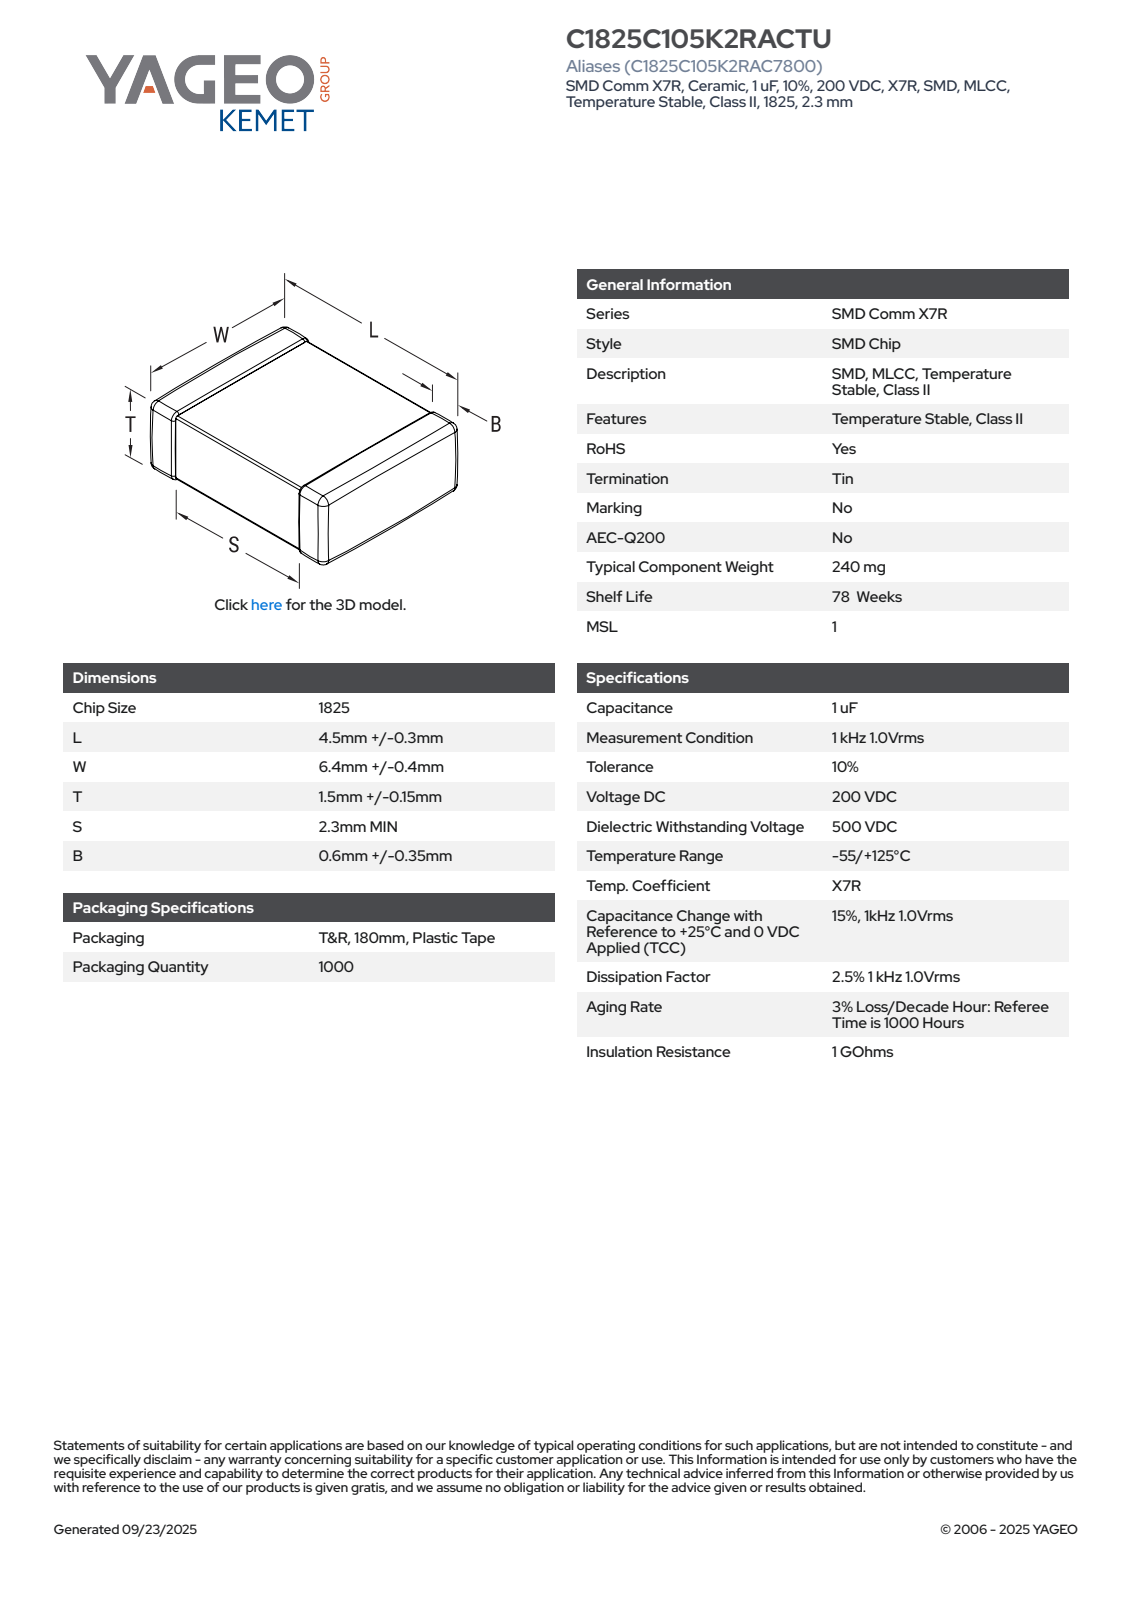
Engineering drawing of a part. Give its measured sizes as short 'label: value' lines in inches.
name: CCS_CCSTDNOS_1825_L4.8W6.8T1.65B0.95
written by: SolidWorks 2014 (AUTOMOTIVE_DESIGN)
unit: in
bodies: 4 solids, 125 faces (71 planar, 38 cylindrical, 16 other)
size: 0.268 × 0.189 × 0.065
volume: 0.003 in³; area: 0.155 in²
rounds: 24× R0.006
face distances: 0.054, 0.059, 0.189, 0.065, 0.262, 0.257, 0.268, 0.013, 0.14, 0.135
